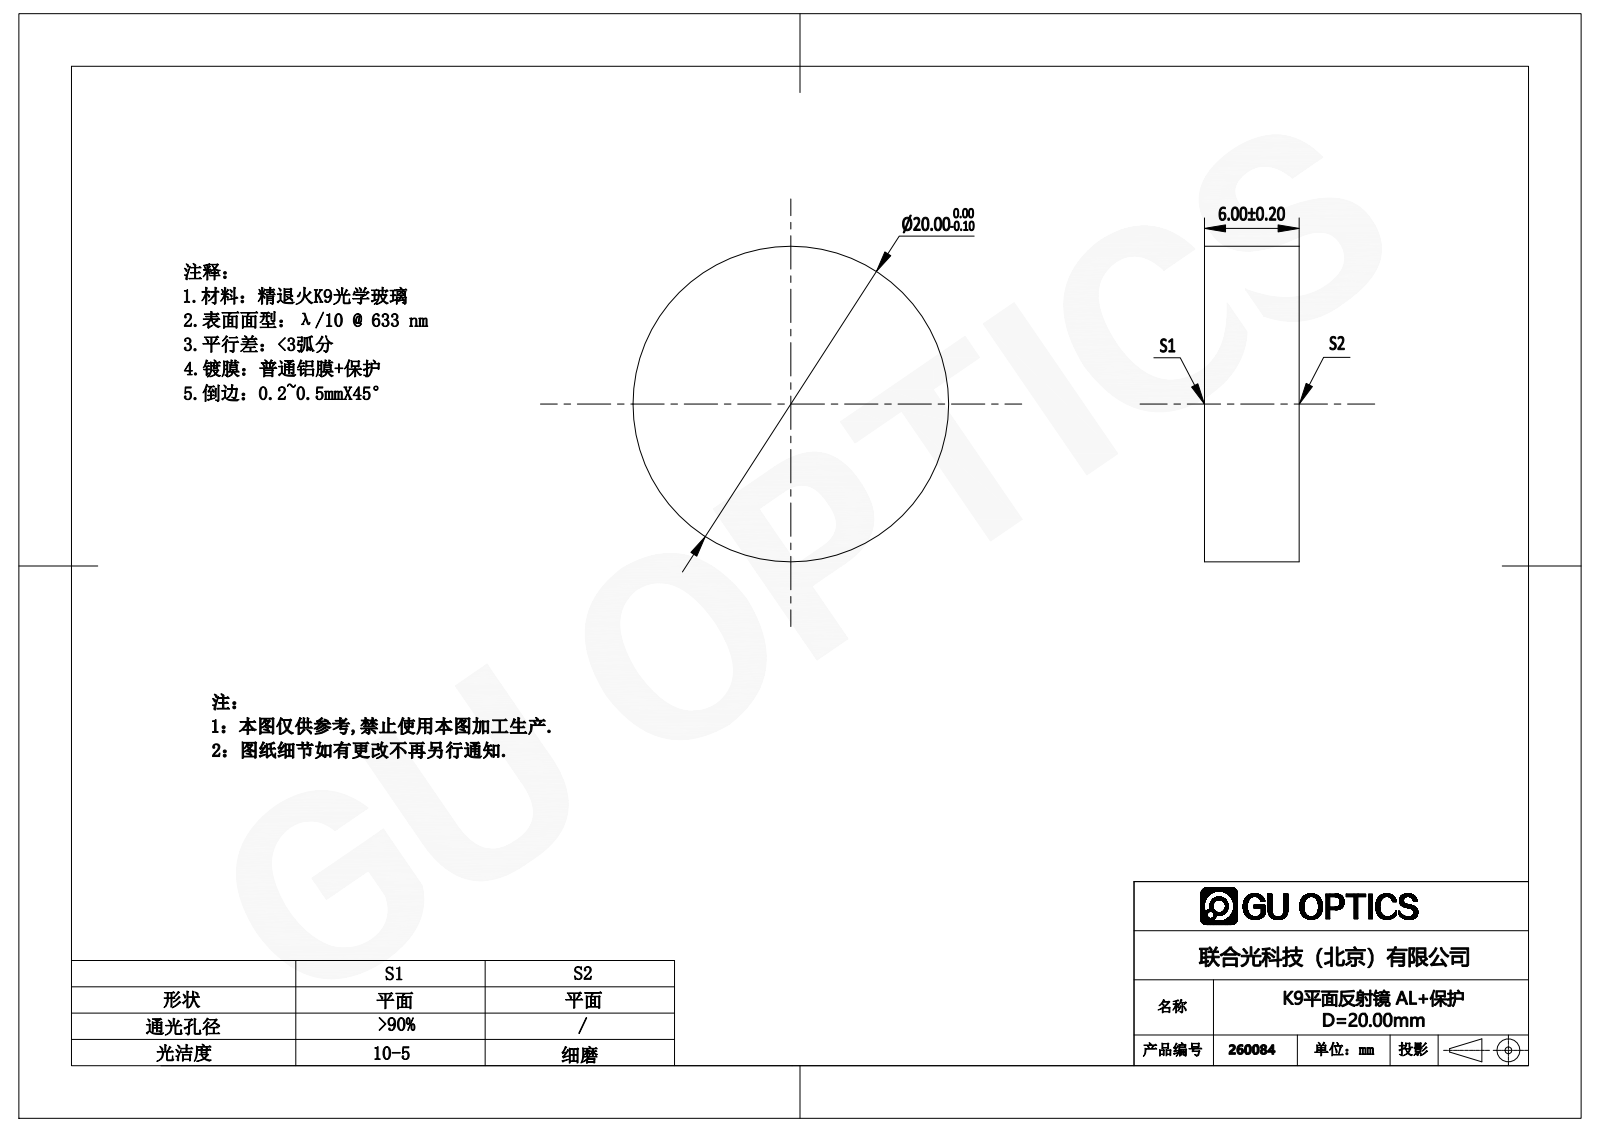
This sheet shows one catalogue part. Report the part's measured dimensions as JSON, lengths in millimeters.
{"part_name": "260071", "step_written_by": "SolidWorks 2016 (AUTOMOTIVE_DESIGN)", "units": "millimeters", "bodies": {"solids": 1, "faces": 4, "planar": 2, "cylindrical": 2, "other": 0}, "overall_size": [20, 20, 6], "volume_mm3": 1885, "surface_area_mm2": 1005, "round_bosses_or_shafts": [[20, 1]], "face_to_face_distances": [6]}
